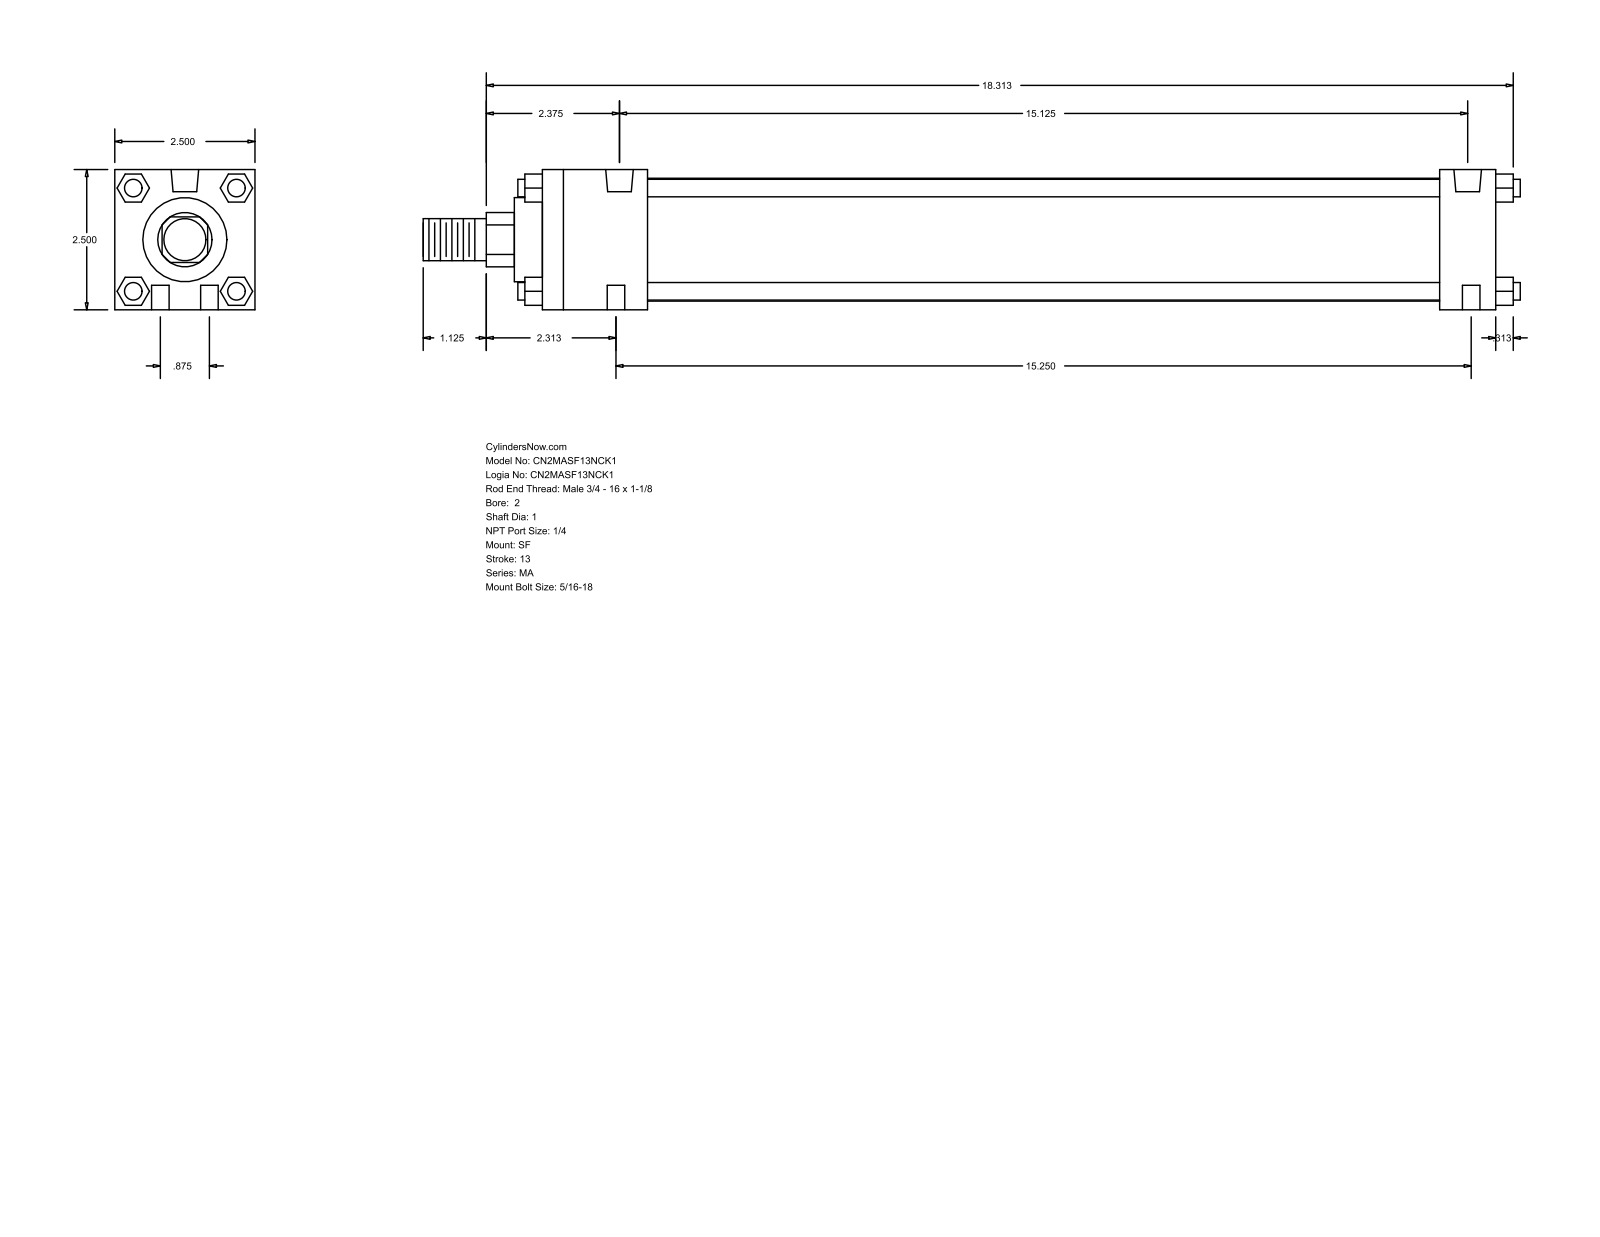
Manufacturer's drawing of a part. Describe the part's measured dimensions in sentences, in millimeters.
The part is named "MA_SF__0200_1". Its 3-D file was written by "GSSL Pune (CONFIG_CONTROL_DESIGN)". It is 0 solids with 124 faces: 94 planar, 30 cylindrical and 0 other. Overall it measures 496.89 by 63.5 by 63.5 millimeters. Round holes: 6 of diameter 7.94, 2 of diameter 12.49. Round bosses or shafts: 4 of diameter 7.94, 1 of diameter 55.63, 1 of diameter 38.1, 1 of diameter 25.4, 1 of diameter 19.05. Partial cylindrical surfaces (rounded edges, fillets, slot ends): 1 of radius 12.29. The main face-to-face distances are 63.5, 431.8, 12.7, 25.4, 406.4, 47.63, 358.77, 384.17, 23.37, 40.47. The hole center spacings are 11.22, 385.92, 22.22, 384.17, 387.35, 387.99.
